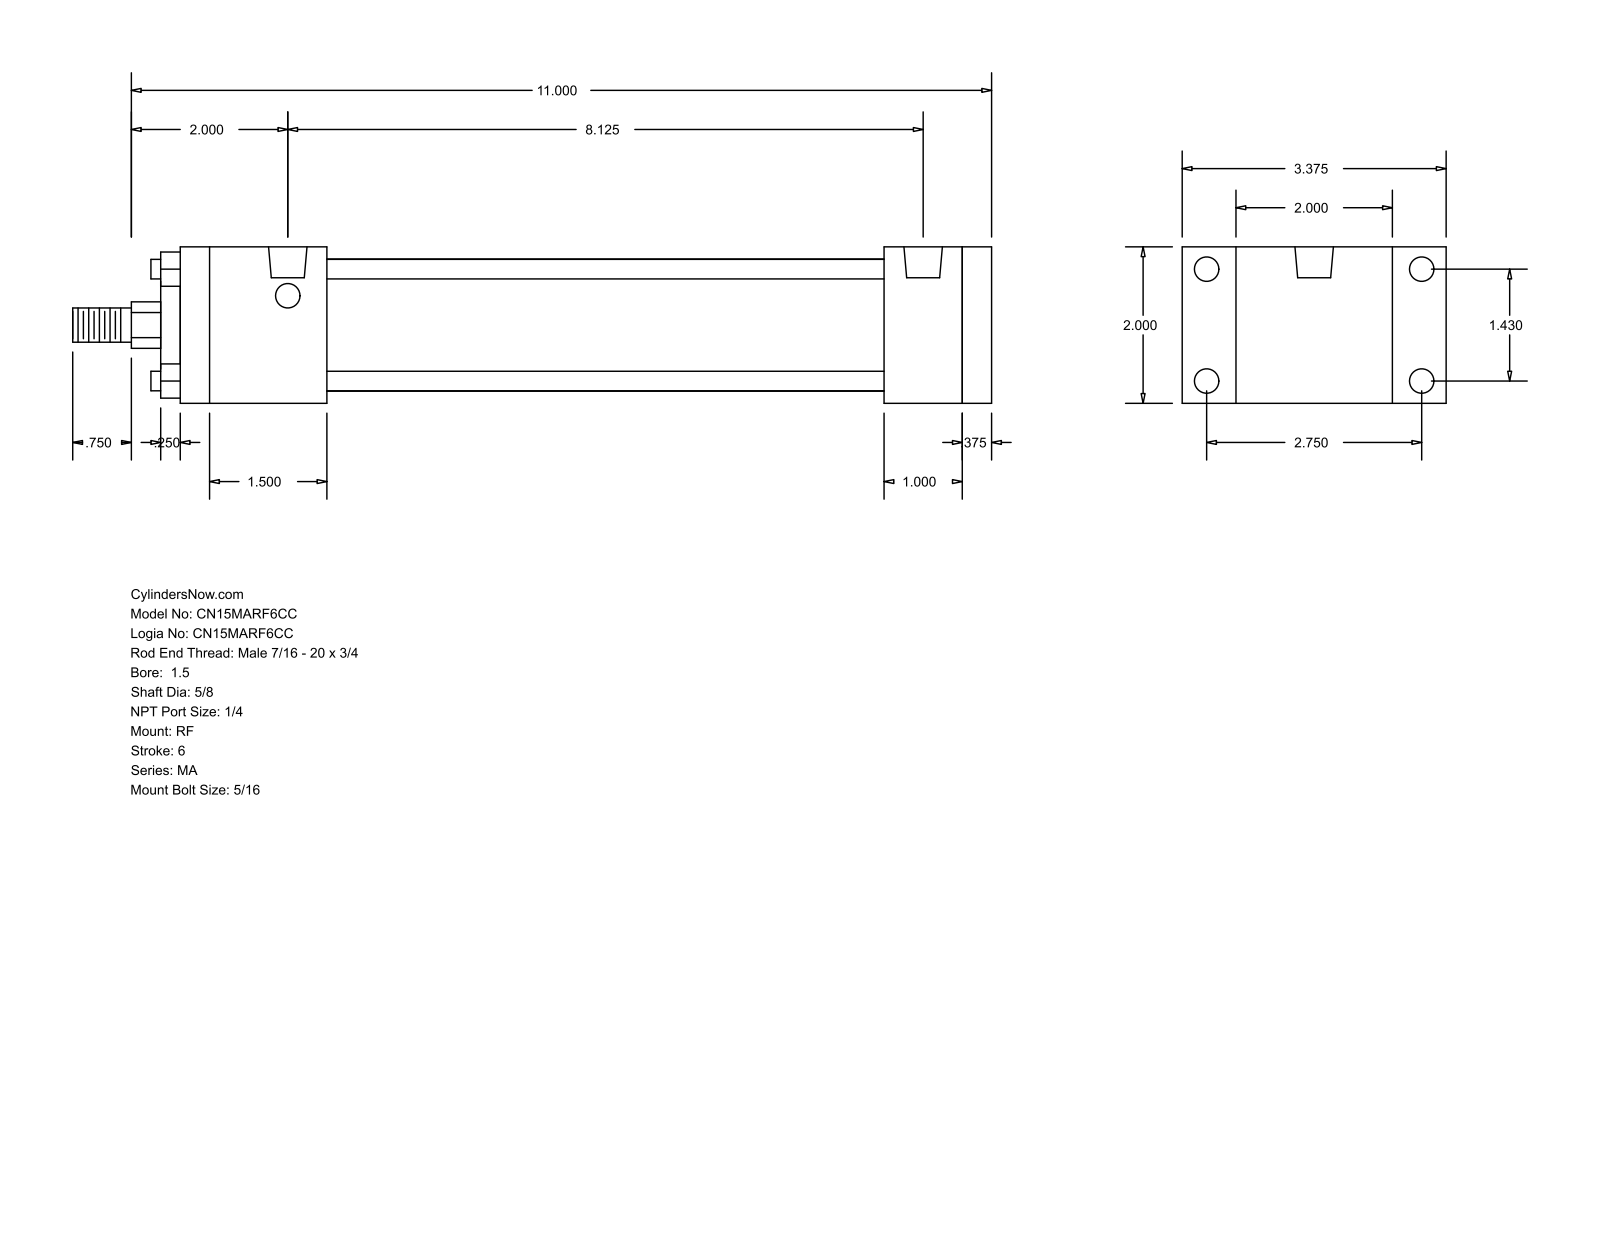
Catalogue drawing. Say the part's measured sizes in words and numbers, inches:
The part is named "MA_RF__0150_0.625". Its 3-D file was written by "GSSL Pune (CONFIG_CONTROL_DESIGN)". It is 0 solids with 92 faces: 64 planar, 28 cylindrical and 0 other. Overall it measures 11.75 by 3.375 by 2 inches. Round holes: 8 of diameter 0.313, 2 of diameter 0.492. Round bosses or shafts: 4 of diameter 0.25, 1 of diameter 1.69, 1 of diameter 1.125, 1 of diameter 0.625, 1 of diameter 0.437. Partial cylindrical surfaces (rounded edges, fillets, slot ends): 1 of radius 0.297. The main face-to-face distances are 2, 10.375, 0.375, 10, 1.375, 9, 1, 1.875, 7.125, 8.125. The hole center spacings are 1.43, 2.75, 3.099, 8.125.
